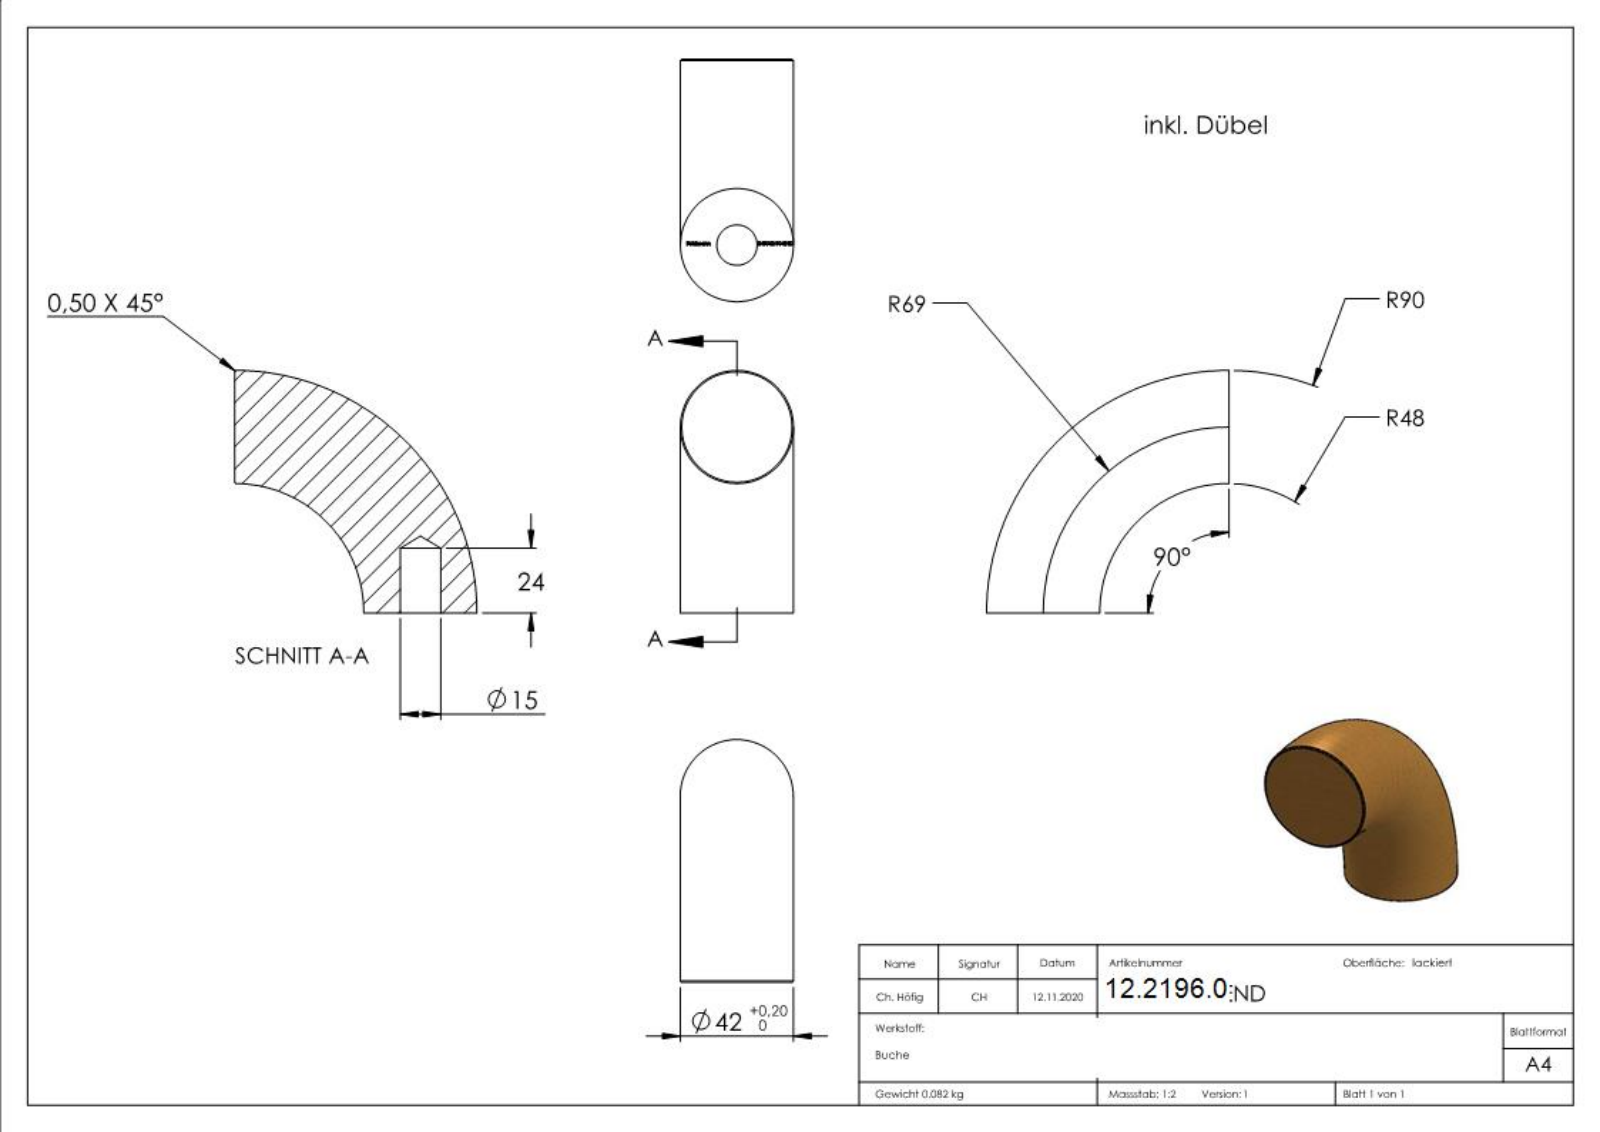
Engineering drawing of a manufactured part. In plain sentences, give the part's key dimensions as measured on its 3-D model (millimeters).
The part is named "H-BU42-90-END". Its 3-D file was written by "SolidWorks 2018 (CONFIG_CONTROL_DESIGN)". It is 1 solid with 278 faces: 175 planar, 2 cylindrical and 101 other. Overall it measures 90 by 90 by 42 millimeters. Its volume is 145 560 cubic millimeters and its surface area 18 165 square millimeters. Round holes: 1 of diameter 15. The main face-to-face distances are 69, 0.44, 0.58, 0.64, 0.34, 0.78, 0.46, 0.68, 0.88, 1.36.
